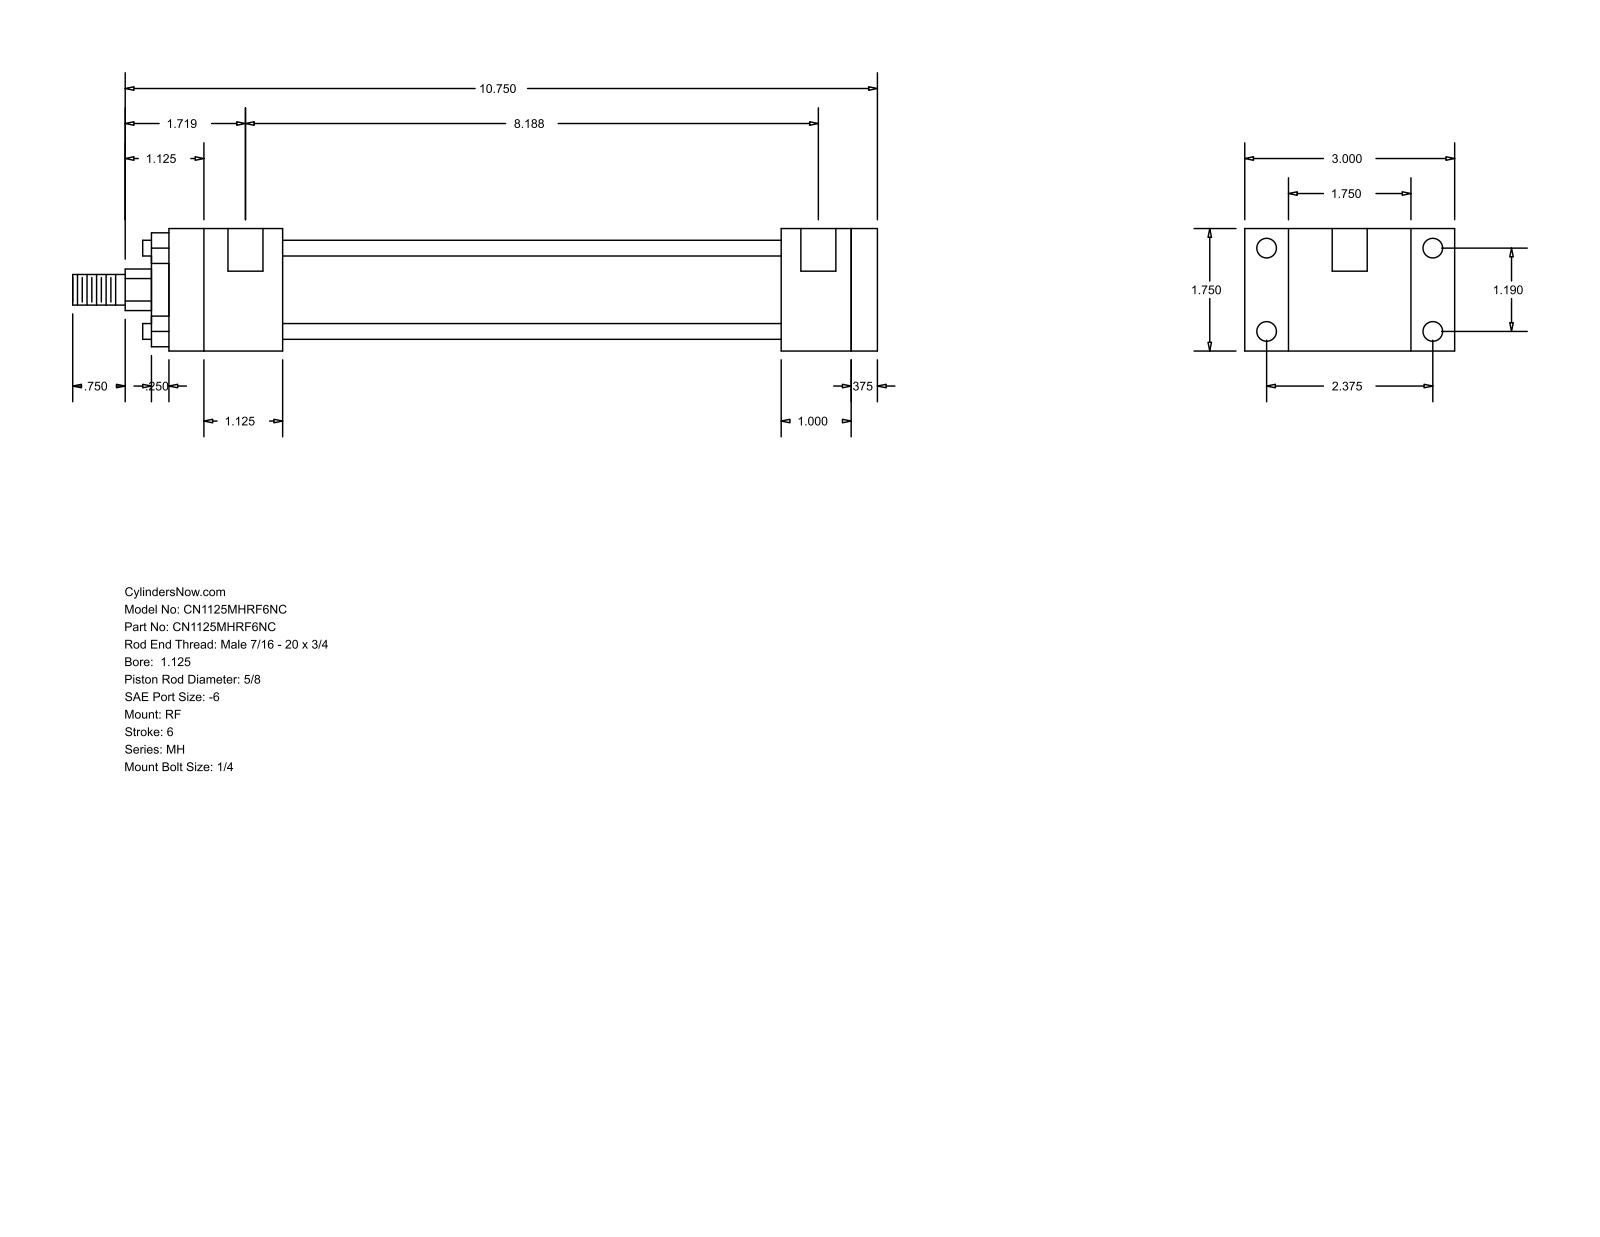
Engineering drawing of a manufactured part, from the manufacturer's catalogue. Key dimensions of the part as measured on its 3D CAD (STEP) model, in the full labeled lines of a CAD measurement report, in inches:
Part name (STEP PRODUCT): MH_RF__0112_0.625
STEP written by: GSSL Pune (CONFIG_CONTROL_DESIGN)
Units: inches
Bodies: 0 solids, 92 faces (64 planar, 28 cylindrical, 0 other)
Overall size (bounding box): 11.5 × 3 × 1.75
Round holes (diameter × count): ⌀0.219 ×4, ⌀0.281 ×4, ⌀0.5 ×2
Round bosses / shafts (diameter × count): ⌀0.225 ×4, ⌀1.375 ×1, ⌀1.125 ×1, ⌀0.625 ×1, ⌀0.437 ×1
Partial cylindrical surfaces — rounded edges, fillets, slot ends (radius × count): R0.297 ×1
Main face-to-face distances: 1.75, 0.375, 10.125, 1, 1.375, 0.625, 8.125, 8.5, 7.125, 1.625
Hole centre spacings: 1.19, 2.375, 2.656, 8.063, 0.125, 8.187
